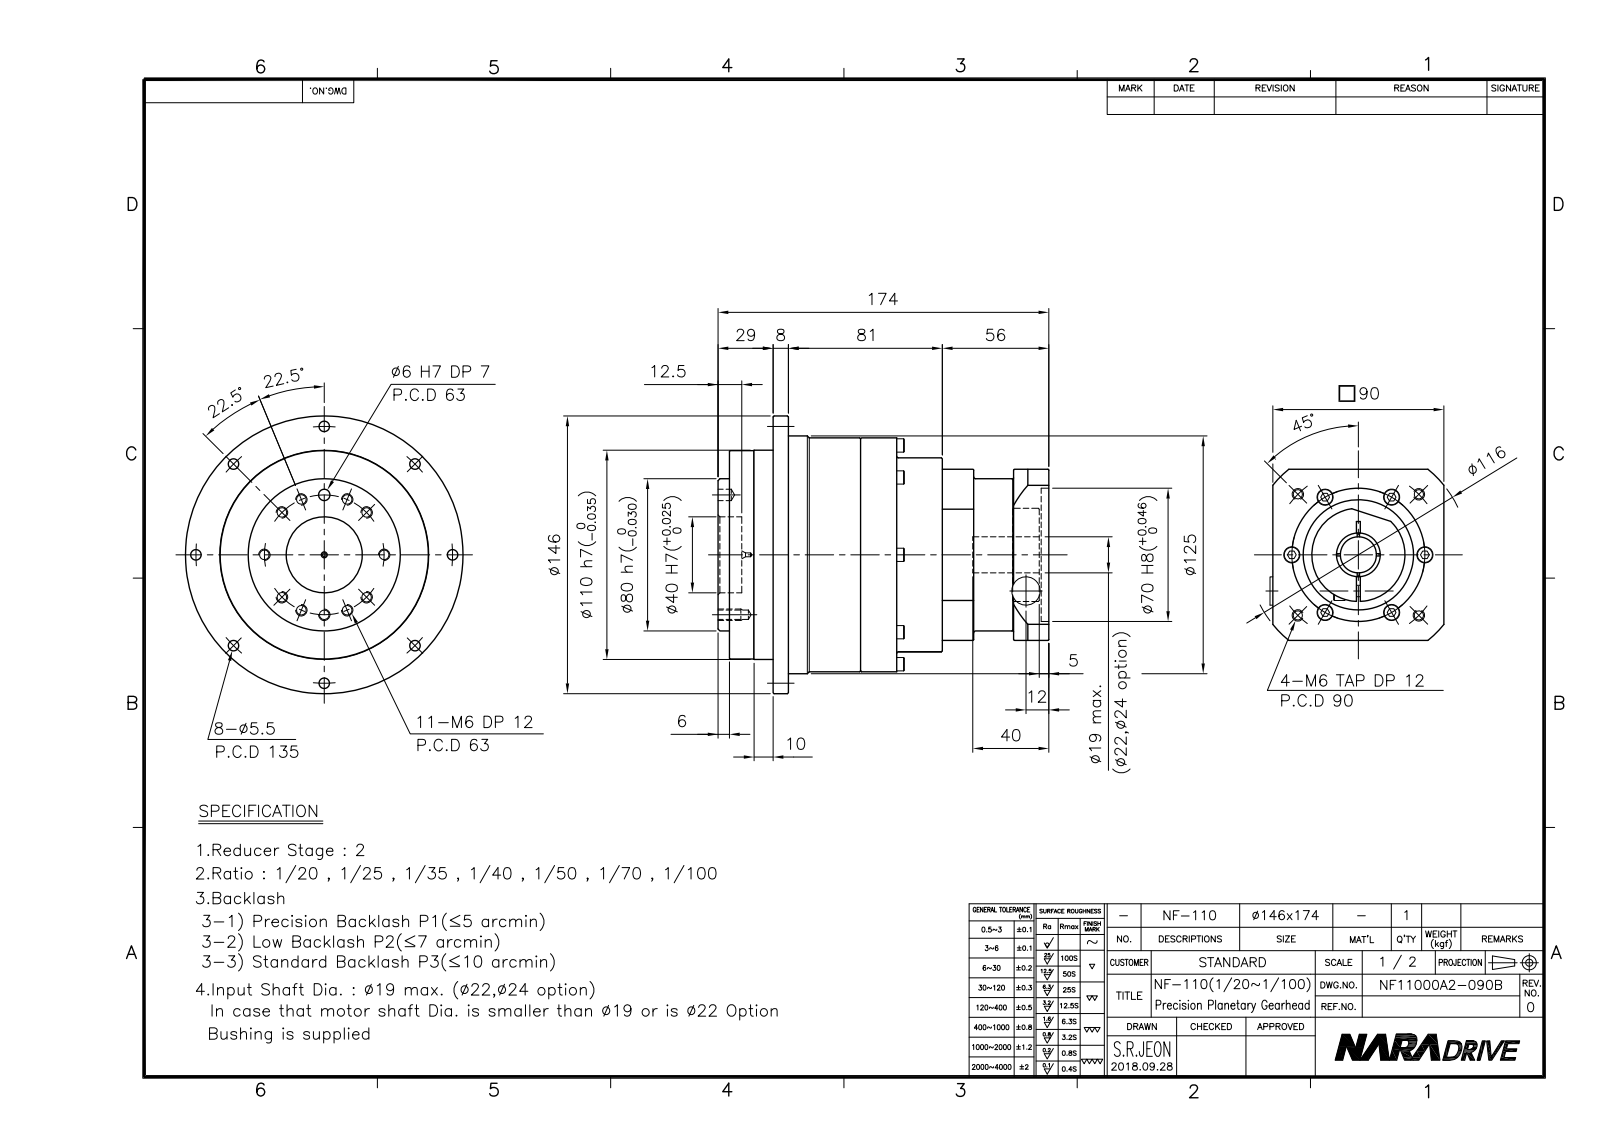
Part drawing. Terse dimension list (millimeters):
name: NF11000A2-090B
written by: Autodesk Inventor 2015 (AUTOMOTIVE_DESIGN)
unit: mm
bodies: 2 solids, 626 faces (287 planar, 178 cylindrical, 161 other)
size: 174 × 146 × 146
volume: 1 107 000 mm³; area: 183 952 mm²
holes: 18× ⌀5.5, 16× ⌀4.92, 10× ⌀4.13, 10× ⌀9, 8× ⌀3.24, 8× ⌀4.5, 1× ⌀2, 1× ⌀6, 1× ⌀6.6, 1× ⌀7, 1× ⌀8.5, 1× ⌀19
bosses: 10× ⌀8.5, 10× ⌀5, 8× ⌀7, 8× ⌀4, 1× ⌀146, 1× ⌀125, 1× ⌀123, 1× ⌀110
rounds: 16× R0.5, 8× R4.5, 1× R5.5, 1× R35, 1× R51, 1× R58
face distances: 8, 19, 38, 75, 46, 99, 56, 87.8, 79.8, 41.8
hole spacings: 35, 51.66, 67.5, 95.46, 31.5, 60.62, 62.62, 40.25
